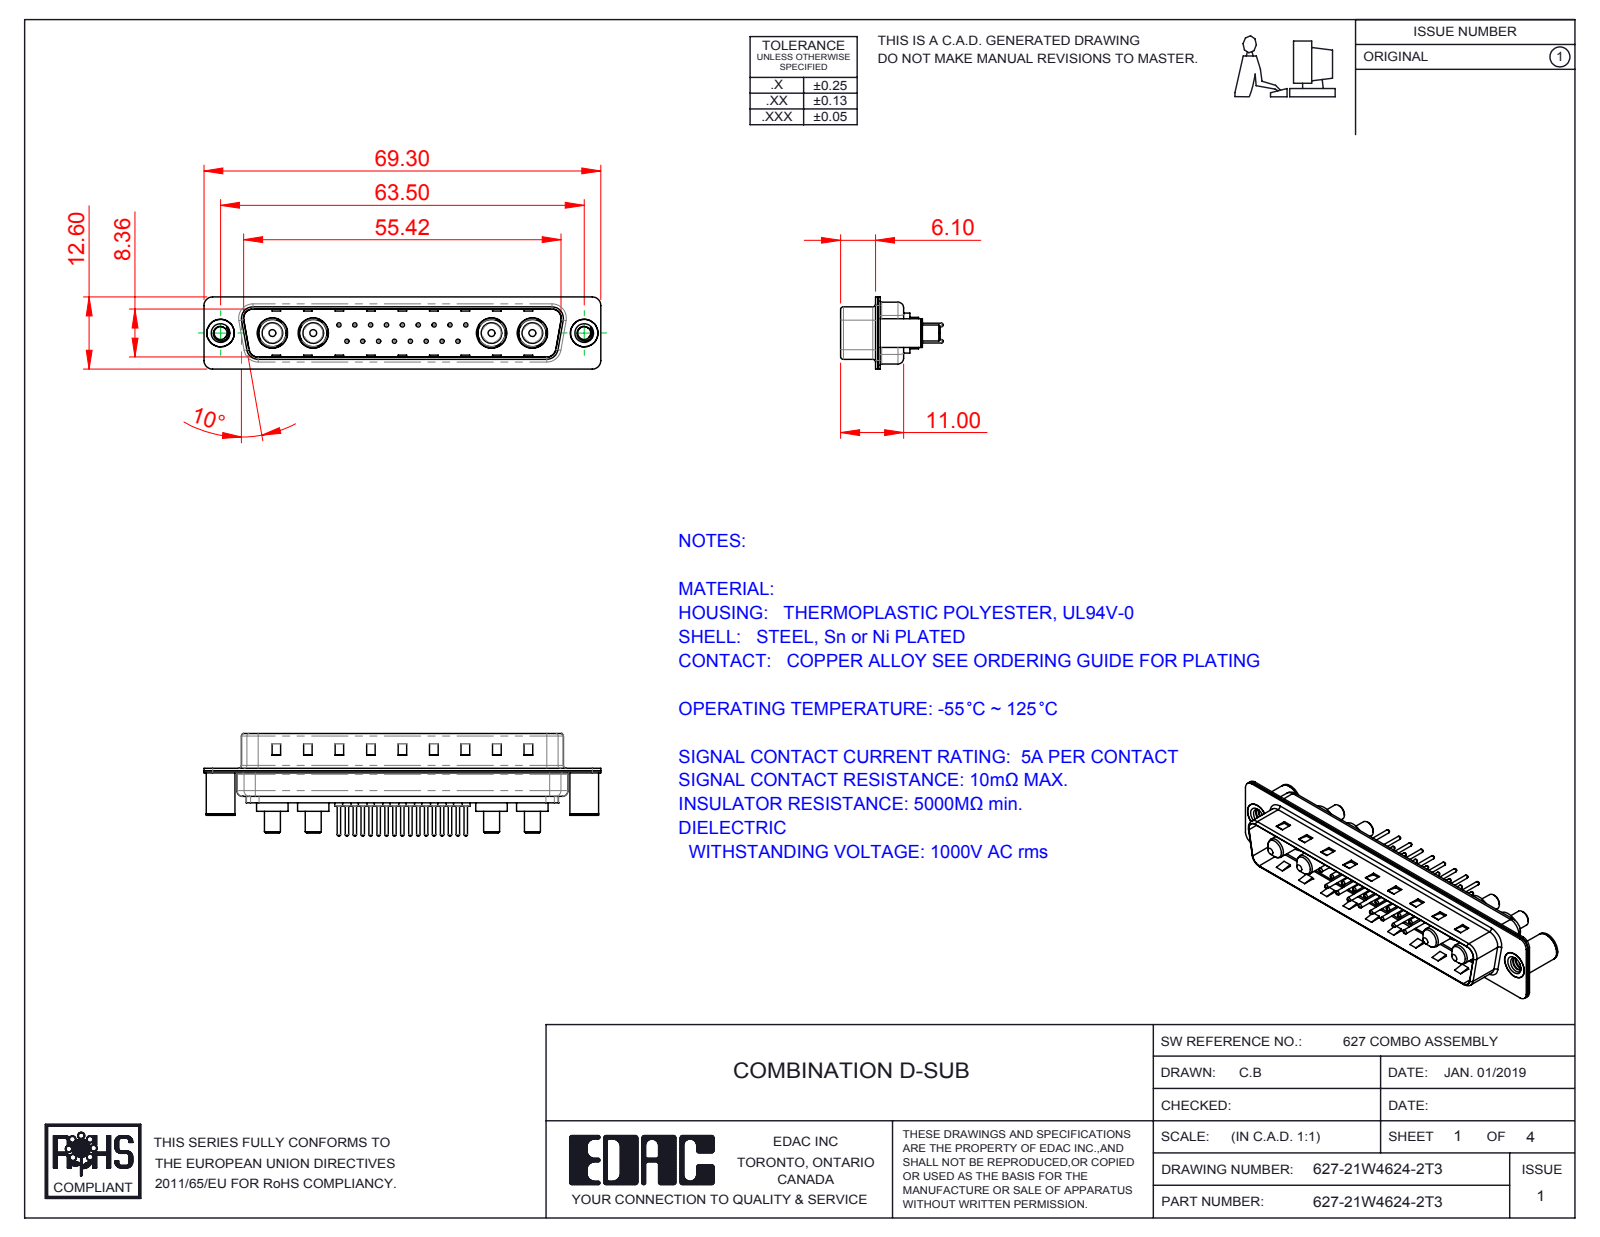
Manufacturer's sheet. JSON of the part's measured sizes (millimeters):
{"part_name": "627Combo Shell Front_37 Contacts; 627Combo Housing_21W4; 627Combo Shell Rear_37 Contacts; Power Pin_20A S (+4 more)", "step_written_by": "SolidWorks 2016 (CONFIG_CONTROL_DESIGN)", "units": "millimeters", "bodies": {"solids": 30, "faces": 1235, "planar": 362, "cylindrical": 479, "other": 394}, "overall_size": [69.3, 17.9, 12.6], "volume_mm3": 4165, "surface_area_mm2": 9401, "round_holes": [[0.75, 17], [1.6, 17], [2, 17], [4.85, 4], [5.3, 4], [2.26, 2], [3.26, 2], [4, 2], [4.8, 2]], "round_bosses_or_shafts": [[1.5, 17], [0.6, 17], [5.5, 4], [5.2, 4], [4.75, 4], [3.75, 4], [3.6, 4], [2.8, 4]], "partial_cylinders_radius": [[1.5, 16], [2, 12], [0.5, 8], [1.6, 8], [0.25, 4], [0.6, 4], [0.65, 4], [0.9, 4]], "face_to_face_distances": [0.4, 0.82, 9.58, 8.76, 1.5, 5.6, 1.22, 9.98, 0.42, 9.18], "hole_center_spacings": [3.16, 2.77, 5.54, 8.31, 5.03, 5.04, 7.49, 10.11]}
